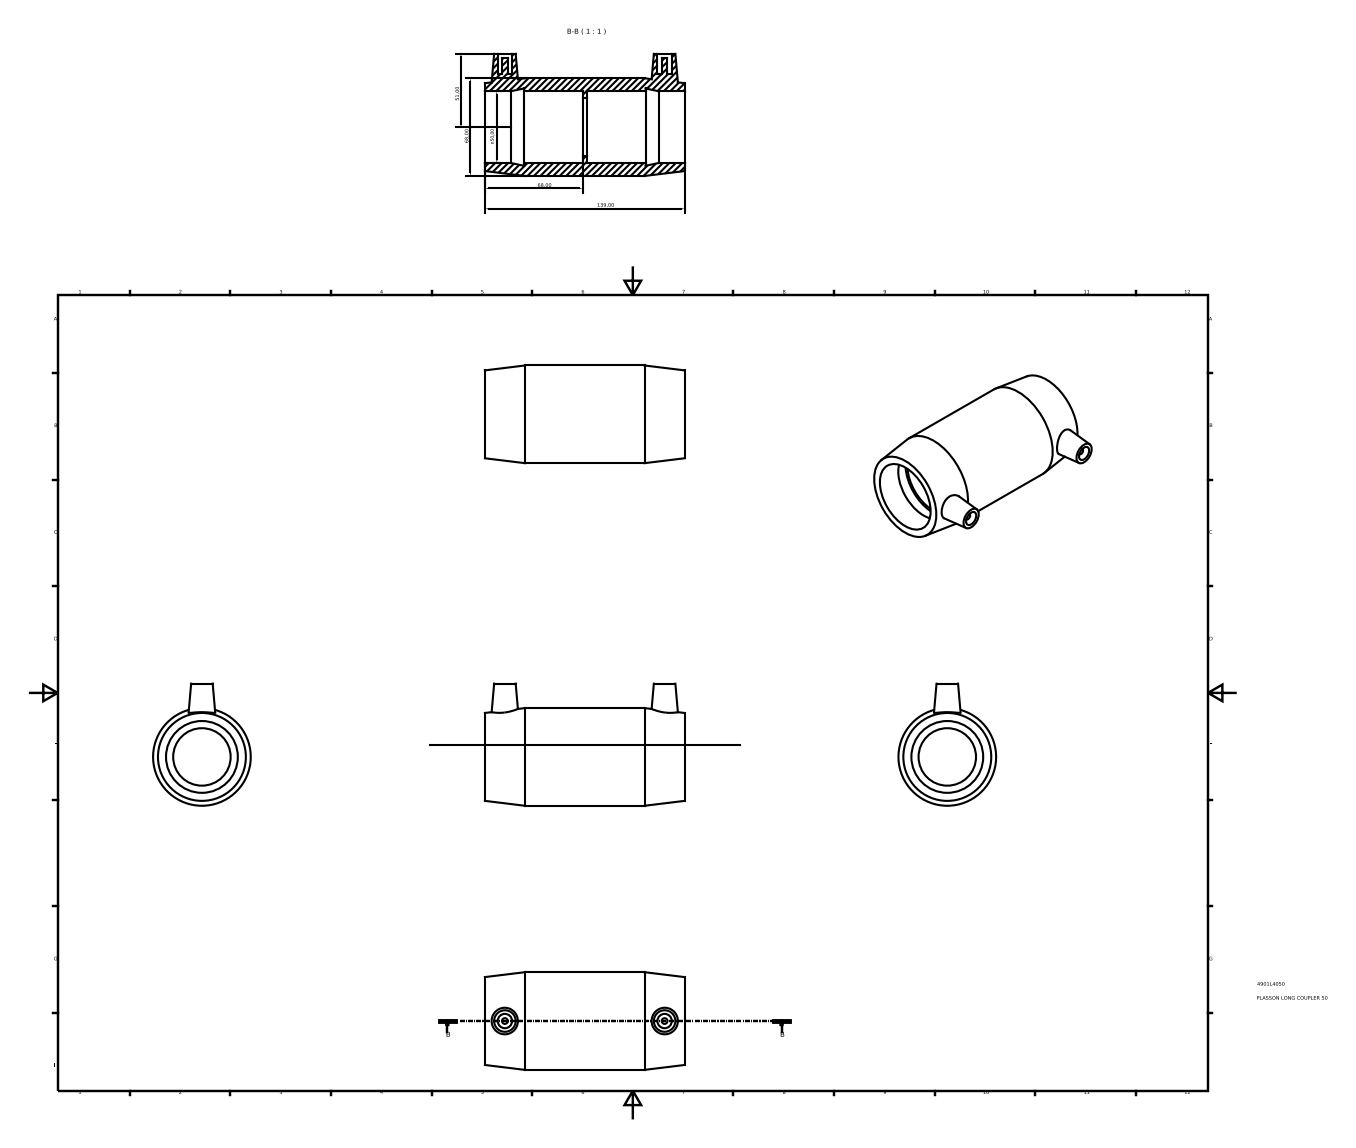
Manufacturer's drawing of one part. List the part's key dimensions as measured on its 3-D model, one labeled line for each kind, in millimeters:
Part name (STEP PRODUCT): 4901L4050
STEP written by: Autodesk Inventor 2015 (AUTOMOTIVE_DESIGN)
Units: millimetres
Bodies: 1 solid, 28 faces (12 planar, 10 cylindrical, 6 other)
Overall size (bounding box): 139 × 85 × 68
Volume: 218 076 mm³ · Surface area: 58 109 mm²
Round holes (diameter × count): ⌀10 ×2, ⌀40 ×1, ⌀50 ×1
Round bosses / shafts (diameter × count): ⌀4 ×2, ⌀68 ×1
Main face-to-face distances: 68, 71, 139, 3, 27.2, 111.8, 40.8, 43.8, 84.6, 14
Hole centre spacings: 111.2
